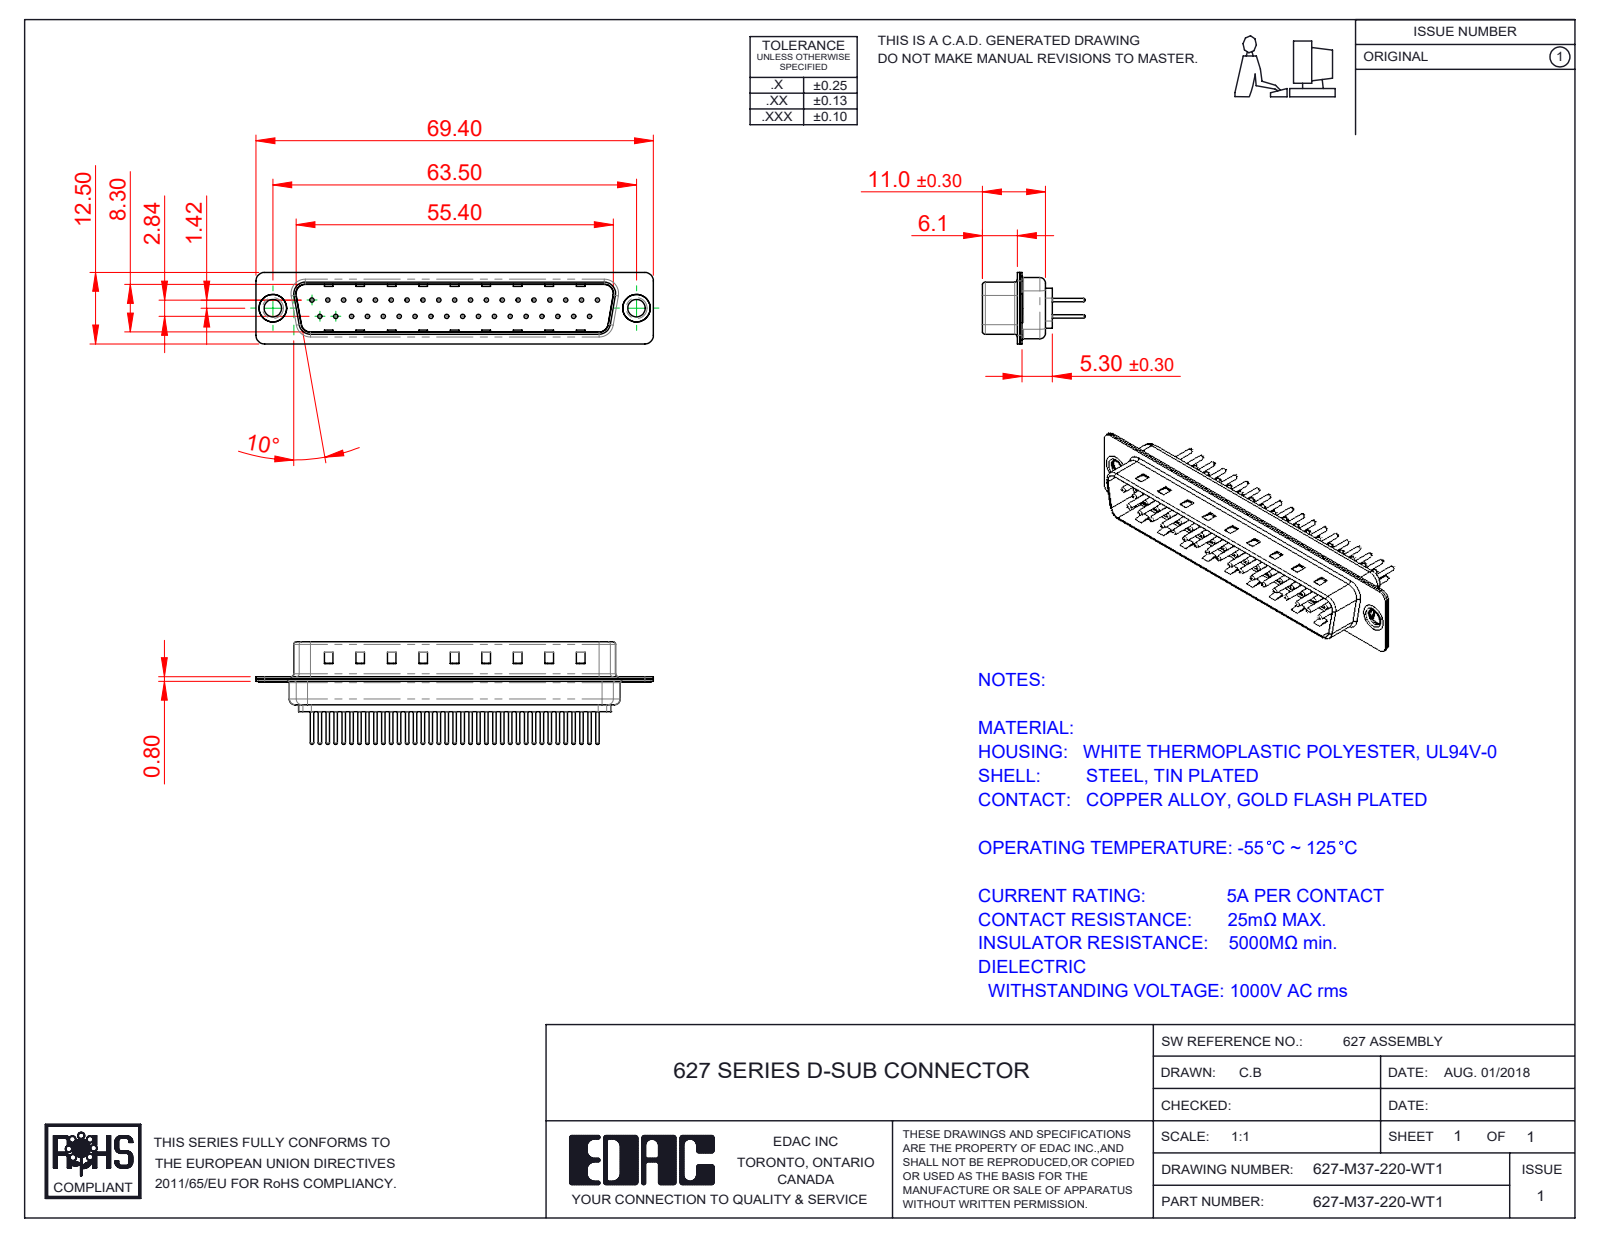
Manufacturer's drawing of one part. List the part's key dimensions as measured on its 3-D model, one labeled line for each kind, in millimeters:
Part name (STEP PRODUCT): 627M Housing_37 Contacts; 627-M37-220-WT1; 627M Contact Row 2_20; 627M Shell Front_37 Contacts (+3 more)
STEP written by: SolidWorks 2020 (CONFIG_CONTROL_DESIGN)
Units: millimetres
Bodies: 42 solids, 1755 faces (462 planar, 643 cylindrical, 650 other)
Overall size (bounding box): 69.4 × 17.9 × 12.5
Volume: 3 690 mm³ · Surface area: 9 124 mm²
Round holes (diameter × count): ⌀0.75 ×37, ⌀1.6 ×37, ⌀2 ×37, ⌀3.05 ×2, ⌀4 ×2, ⌀4.8 ×2
Round bosses / shafts (diameter × count): ⌀1.5 ×37, ⌀0.6 ×37, ⌀5 ×2, ⌀4.9 ×2, ⌀3.55 ×2
Partial cylindrical surfaces — rounded edges, fillets, slot ends (radius × count): R1.5 ×16, R2 ×12, R0.5 ×8, R1.6 ×8, R0.25 ×4, R0.6 ×4, R0.65 ×4, R0.9 ×4
Main face-to-face distances: 0.4, 0.8, 9.5, 9.1, 8.7, 9.9, 1.2, 5.7, 0.75, 0.35
Hole centre spacings: 2.77, 5.54, 3.16, 8.31, 11.08, 13.85, 16.62, 19.39
